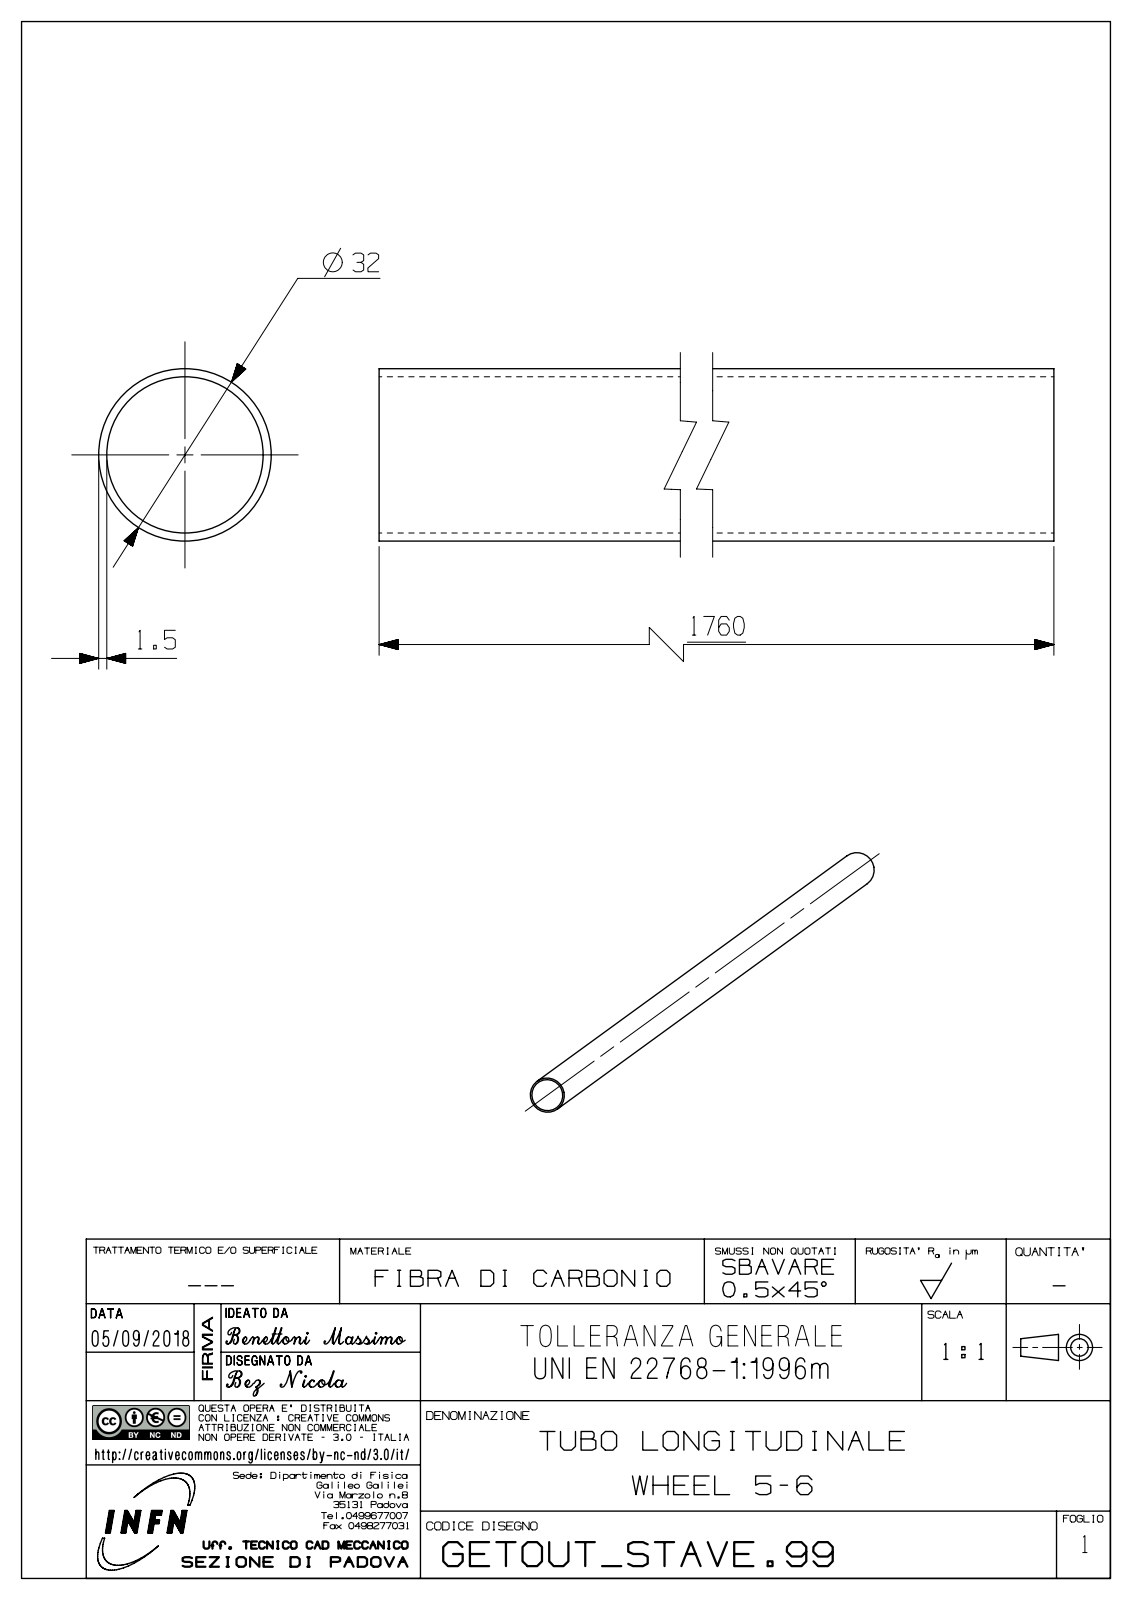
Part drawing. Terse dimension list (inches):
name: bez8324385A6uyz
written by: SIEMENS PLM Software NX 12.0 (AUTOMOTIVE_DESIGN)
unit: in
bodies: 1 solid, 4 faces (2 planar, 2 cylindrical, 0 other)
size: 69.291 × 1.26 × 1.26
volume: 15.44 in³; area: 523.2 in²
holes: 1× ⌀1.142
bosses: 1× ⌀1.26
face distances: 69.291
